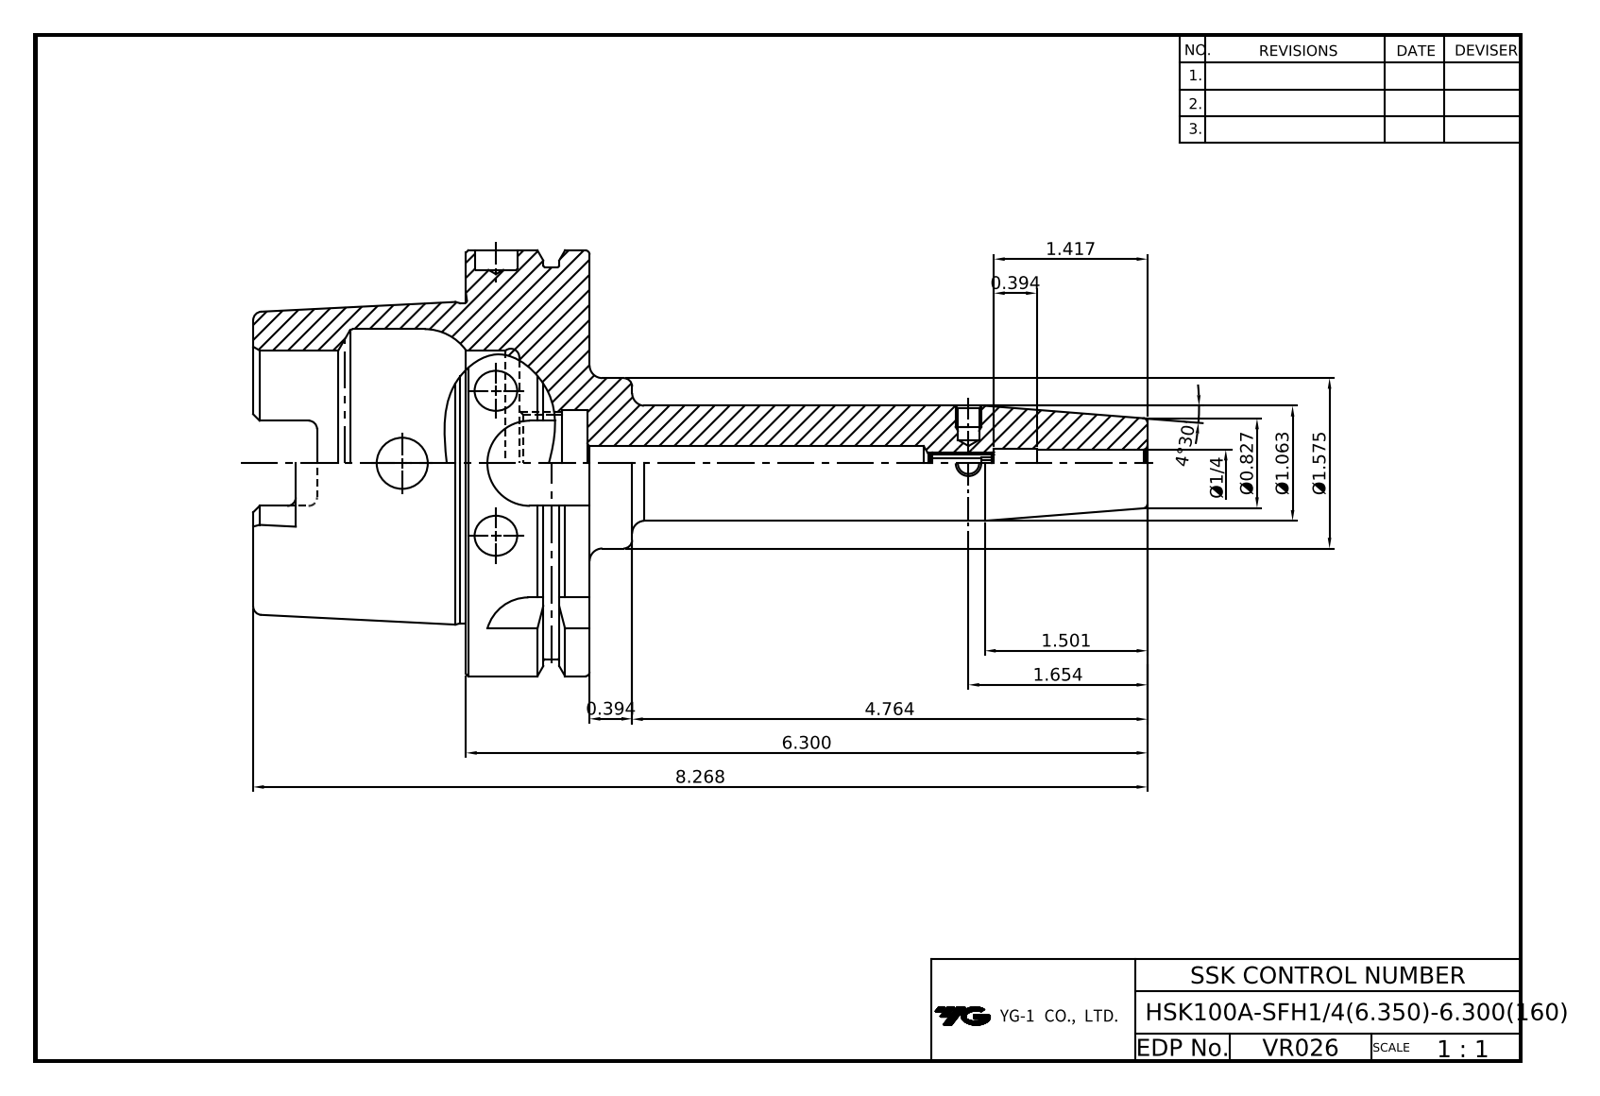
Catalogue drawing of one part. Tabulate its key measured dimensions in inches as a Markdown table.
| quantity | value |
| --- | --- |
| part name | HSK100A-SFH9_525-160 |
| STEP written by | CREO PARAMETRIC BY PTC INC, 2018400 (CONFIG_CONTROL_DESIGN) |
| units | inches |
| bodies | 1 solid, 215 faces (57 planar, 72 cylindrical, 86 other) |
| overall size | 8.268 × 3.937 × 3.937 |
| volume | 20.71 in³ |
| surface area | 107.2 in² |
| round holes (diameter × count) | 0.197 × 2, 0.236 × 2, 0.472 × 2, 0.276 × 1, 0.315 × 1, 0.375 × 1, 0.394 × 1, 0.402 × 1, 0.886 × 1, 0.945 × 1, 0.984 × 1, 2.087 × 1 |
| round bosses / shafts (diameter × count) | 3.937 × 1, 3.622 × 1, 2.959 × 1, 1.575 × 1, 1.26 × 1 |
| partial cylindrical surfaces (radius × count) | 0.079 × 6, 0.192 × 4, 0.394 × 4 |
| main face-to-face distances | 1.142, 0.492, 0.65, 2.461, 3.11, 1.969, 0.394, 2.854, 0.886, 0.256 |
| hole center spacings | 3.898, 4.764 |
